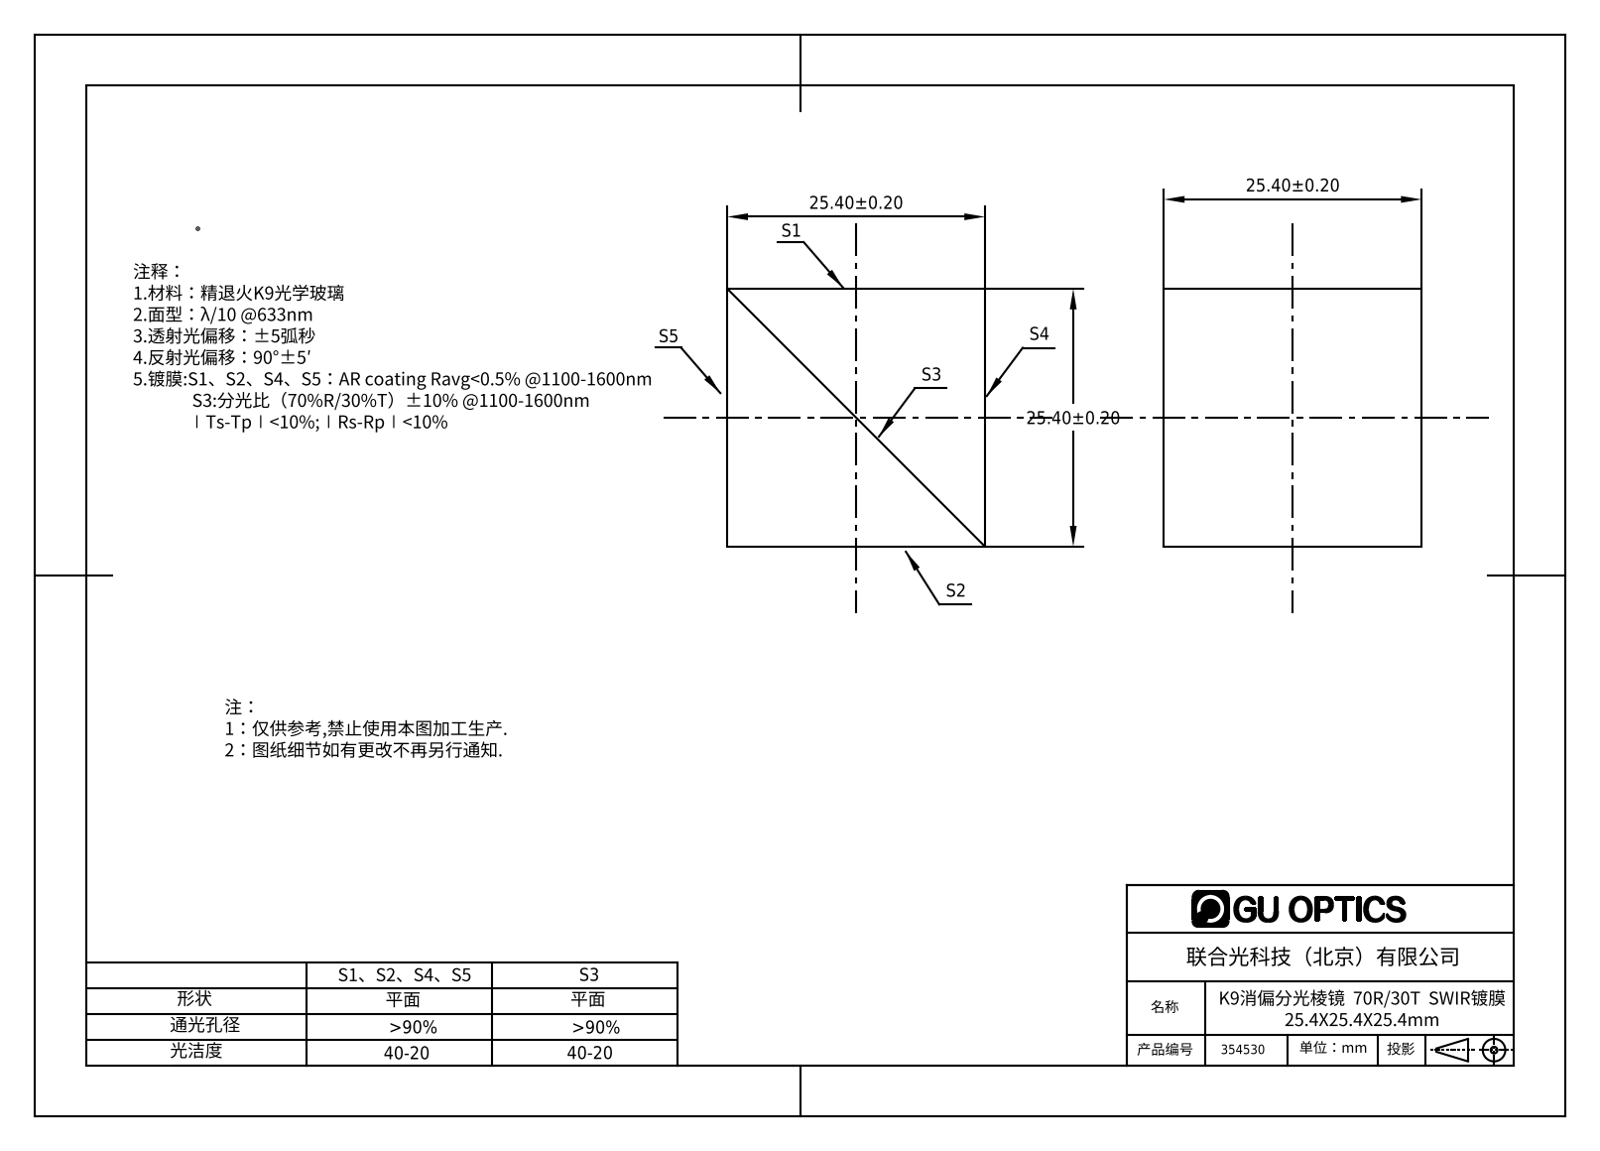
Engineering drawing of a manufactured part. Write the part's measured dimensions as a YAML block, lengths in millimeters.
part_name: "354505"
step_written_by: "SolidWorks 2016 (AUTOMOTIVE_DESIGN)"
units: millimeters
bodies: {solids: 2, faces: 10, planar: 10, cylindrical: 0, other: 0}
overall_size: [25.4, 25.4, 25.4]
volume: 16387
surface_area: 5696
face_to_face_distances: [25.4]
